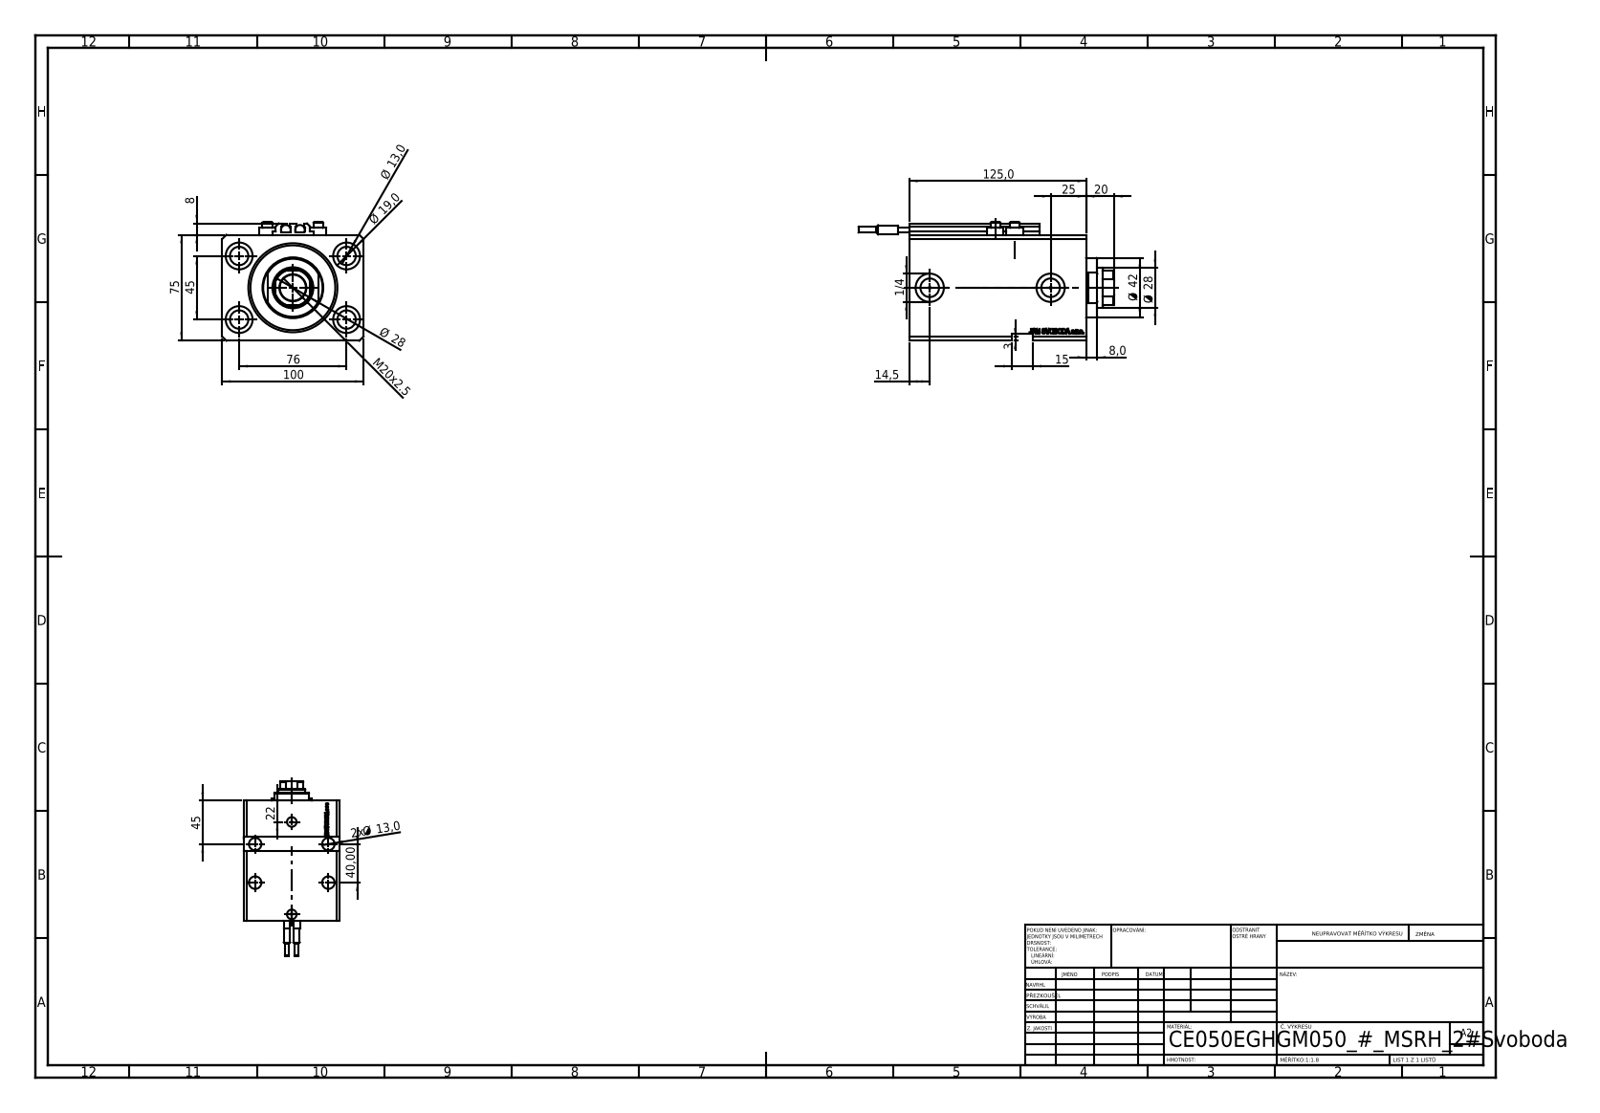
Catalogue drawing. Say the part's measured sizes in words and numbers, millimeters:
The part is named "SWITCH_V250CE; V250CE_C_VCP; ALLEN BOLT V250CE; V250CE_VC_E (+1 more)". Its 3-D file was written by "SolidWorks 2019 (CONFIG_CONTROL_DESIGN)". It is 10 solids with 1160 faces: 567 planar, 158 cylindrical and 435 other. Overall it measures 181 by 100 by 84 millimeters. Its volume is 772 385 cubic millimeters and its surface area 153 100 square millimeters. Round holes: 8 of diameter 13, 4 of diameter 1.25, 4 of diameter 4, 4 of diameter 19, 2 of diameter 10, 2 of diameter 13.16, 2 of diameter 20, 1 of diameter 18.5, 1 of diameter 28, 1 of diameter 50, 1 of diameter 63. Round bosses or shafts: 4 of diameter 11.6, 4 of diameter 7, 2 of diameter 6.8, 2 of diameter 6.5, 2 of diameter 4, 1 of diameter 42. Partial cylindrical surfaces (rounded edges, fillets, slot ends): 10 of radius 0.2, 1 of radius 13.5. The main face-to-face distances are 75, 100, 125, 20, 11.9, 113.1, 105, 93.1, 70, 5. The hole center spacings are 44.16, 76, 13.6, 20.72, 27.59, 29, 33.62, 36.
